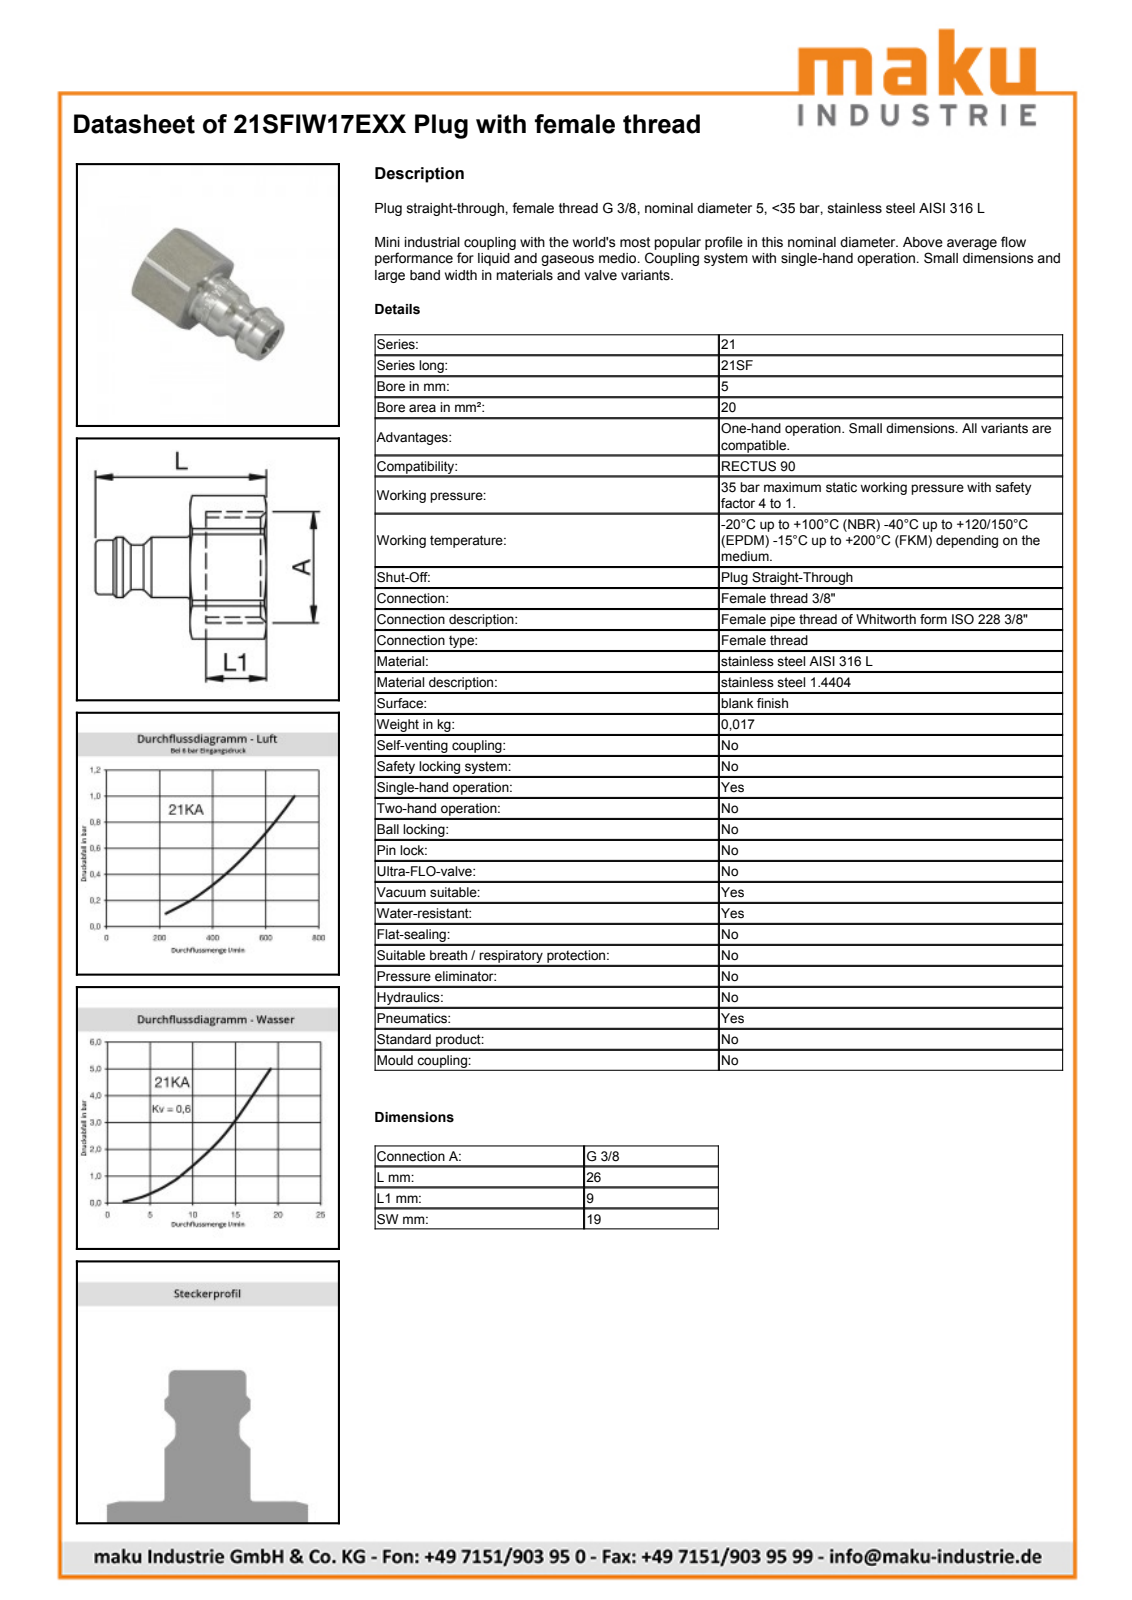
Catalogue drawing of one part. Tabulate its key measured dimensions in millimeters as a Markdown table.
| quantity | value |
| --- | --- |
| part name | D112306 |
| STEP written by | Autodesk Inventor 2013 (AUTOMOTIVE_DESIGN) |
| units | millimeters |
| bodies | 1 solid, 42 faces (10 planar, 12 cylindrical, 20 other) |
| overall size | 25.5 × 21.4 × 19 |
| volume | 3 329 mm³ |
| surface area | 2 202 mm² |
| round holes (diameter × count) | 4.95 × 1, 9.73 × 1 |
| round bosses / shafts (diameter × count) | 9 × 1, 8.1 × 1, 6.65 × 1 |
| partial cylindrical surfaces (radius × count) | 10.7 × 1 |
| main face-to-face distances | 19, 11.4, 2.4, 9, 14.1, 16.5, 25.5 |
